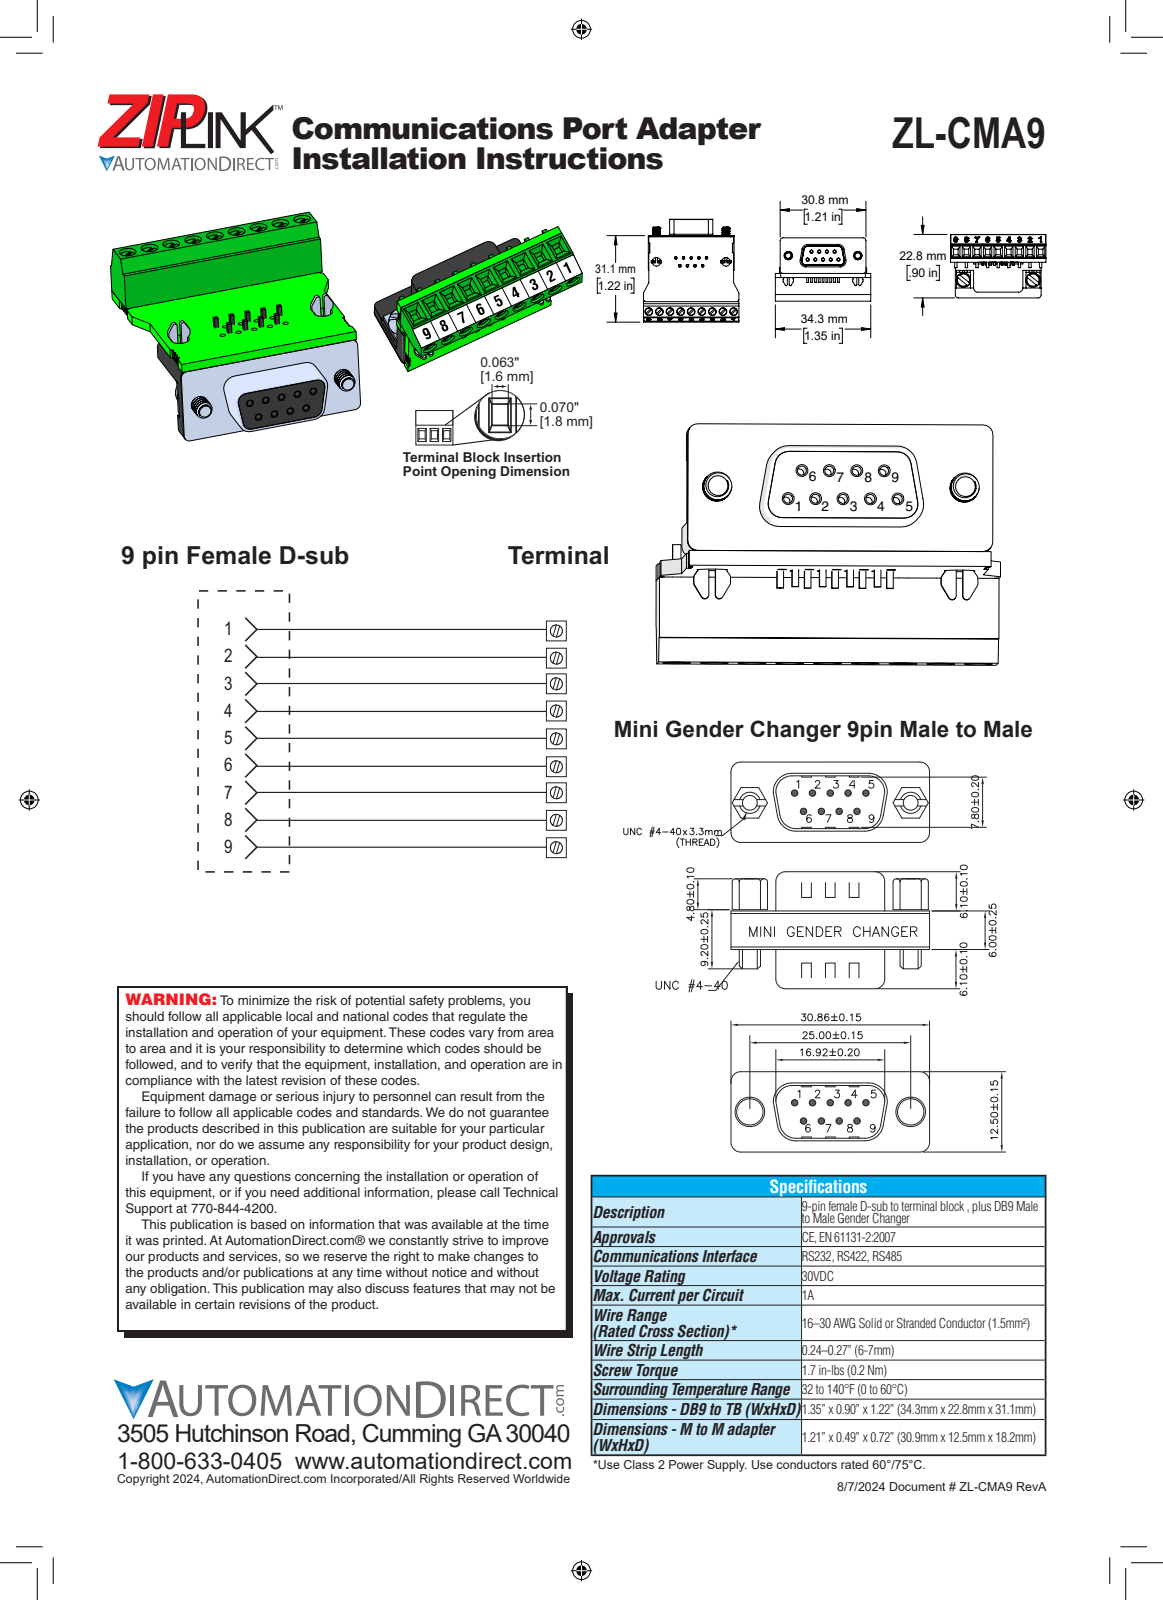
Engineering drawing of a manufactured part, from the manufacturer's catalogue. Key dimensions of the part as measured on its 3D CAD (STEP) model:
Part name (STEP PRODUCT): ZL-CMA9
STEP written by: SolidWorks 2021 (AUTOMOTIVE_DESIGN)
Units: inches
Bodies: 13 solids, 1051 faces (637 planar, 233 cylindrical, 181 other)
Overall size (bounding box): 1.458 × 1.35 × 0.898
Volume: 0.431 in³ · Surface area: 12.88 in²
Round holes (diameter × count): ⌀0.035 ×9, ⌀0.036 ×9, ⌀0.039 ×9, ⌀0.13 ×9, ⌀0.118 ×2, ⌀0.122 ×2
Round bosses / shafts (diameter × count): ⌀0.112 ×2
Partial cylindrical surfaces — rounded edges, fillets, slot ends (radius × count): R0.007 ×16, R0.016 ×16, R0.039 ×8, R0.059 ×6, R0.004 ×4, R0.02 ×4, R0.055 ×4, R0.063 ×4
Main face-to-face distances: 0.059, 0.48, 0.384, 0.12, 0.039, 0.488, 0.932, 0.924, 0.444, 0.114
Hole centre spacings: 0.15, 0.3, 0.45, 0.6, 0.75, 0.124, 0.9, 1.05
